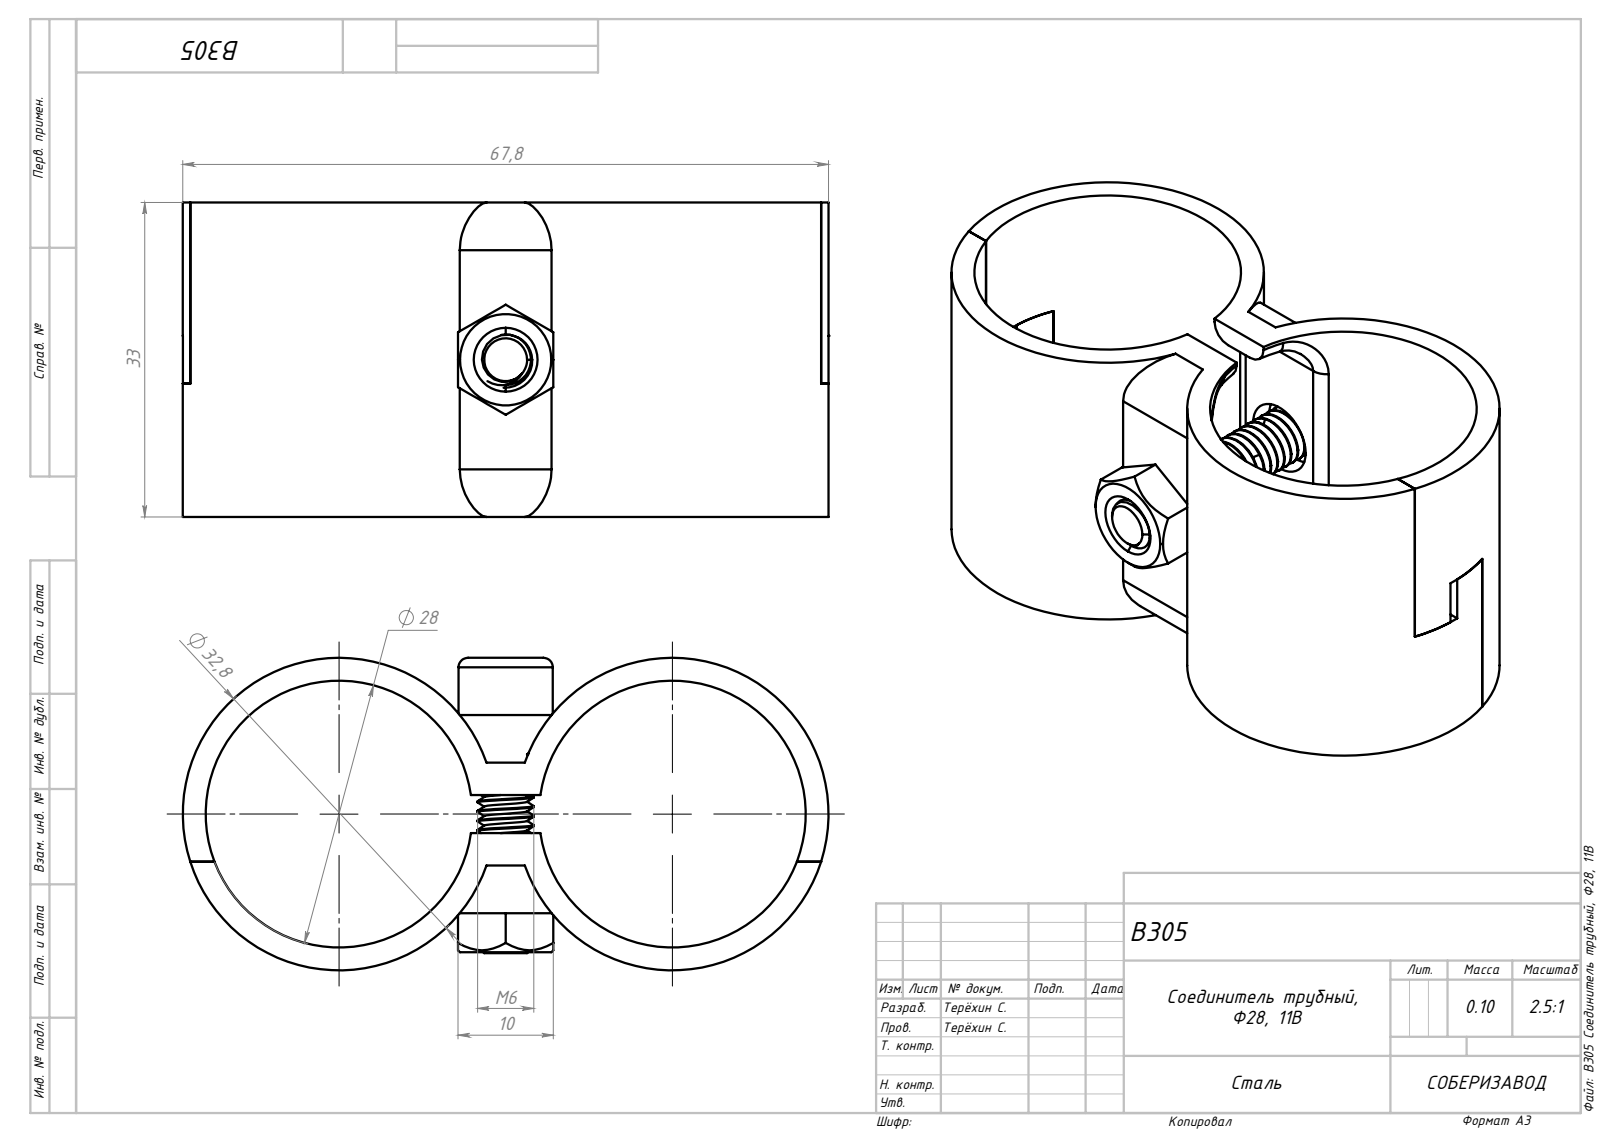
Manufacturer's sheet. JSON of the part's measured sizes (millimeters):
{"part_name": "Сборка8; B305 Соединитель трубный, Ф28, 11B.stp_00; F-180-1.stp_00; D-15.stp_00 (+1 more)", "step_written_by": "SolidWorks 2022 (AUTOMOTIVE_DESIGN)", "units": "millimeters", "bodies": {"solids": 4, "faces": 185, "planar": 56, "cylindrical": 88, "other": 41}, "overall_size": [67.8, 33, 32.8], "volume_mm3": 15088, "surface_area_mm2": 14639, "round_holes": [[28, 2], [5.3, 1], [7.8, 1]], "round_bosses_or_shafts": [[32.8, 2], [9.9, 1], [7, 1], [5.9, 1]], "partial_cylinders_radius": [[0.3, 6], [2, 4], [3, 4], [5, 4]], "face_to_face_distances": [33, 3, 2.4, 5.4, 15.4, 18.4, 13, 10, 20.8, 16], "hole_center_spacings": [35]}
